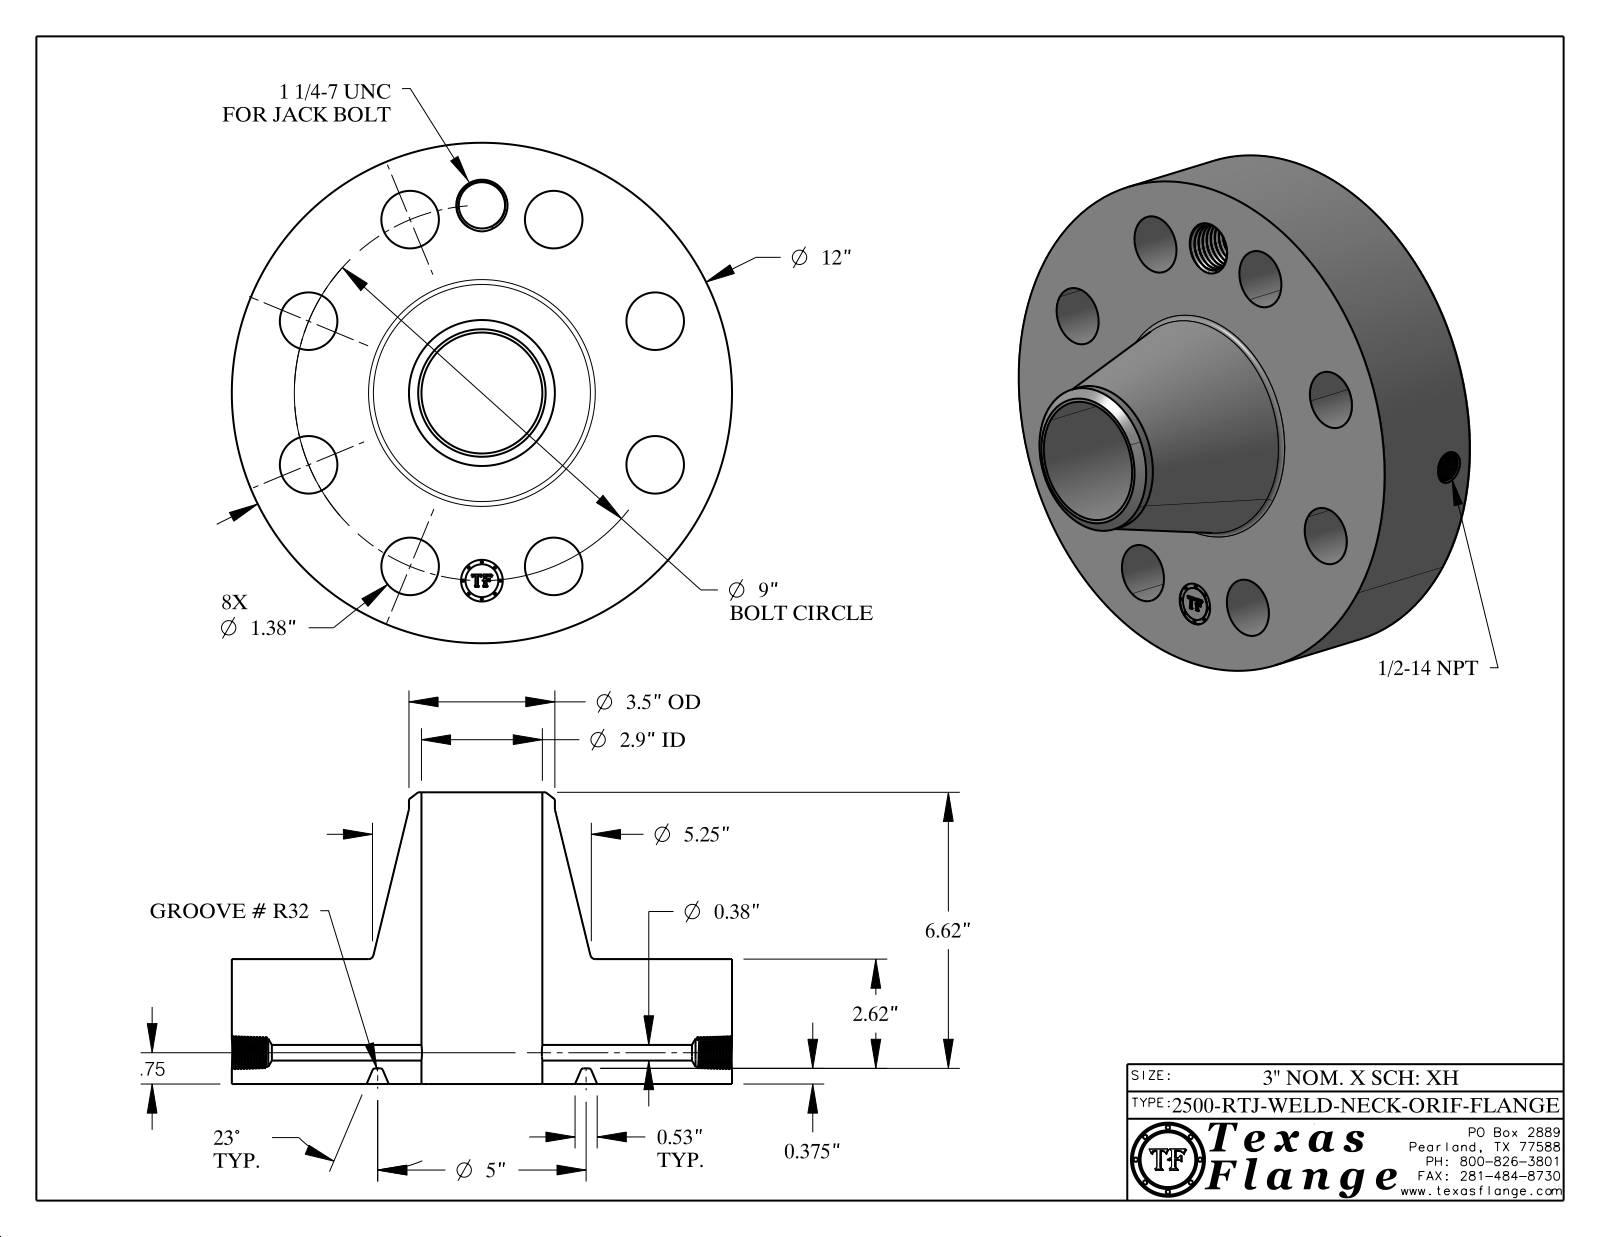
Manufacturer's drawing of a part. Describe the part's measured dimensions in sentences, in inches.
The part is named "2500-RTJ-WELD-NECK". Its 3-D file was written by "CATIA V5 STEP AP214 (AUTOMOTIVE_DESIGN)". It is 1 solid with 813 faces: 370 planar, 103 cylindrical and 340 other. Overall it measures 12 by 12 by 6.995 inches. Its volume is 308.1 cubic inches and its surface area 547.2 square inches. Round holes: 8 of diameter 1.38, 1 of diameter 0.375, 1 of diameter 0.672, 1 of diameter 1, 1 of diameter 1.109, 1 of diameter 2.9. Round bosses or shafts: 8 of diameter 0.061, 1 of diameter 12, 1 of diameter 3.5, 1 of diameter 0.788. The main face-to-face distances are 2.995, 0.375, 2.62, 6.995, 6.62, 4, 2.98, 2.605, 0.015, 4.015. The hole center spacings are 4.5, 3.444, 6.364, 8.315, 9, 1.756, 5, 7.483.
